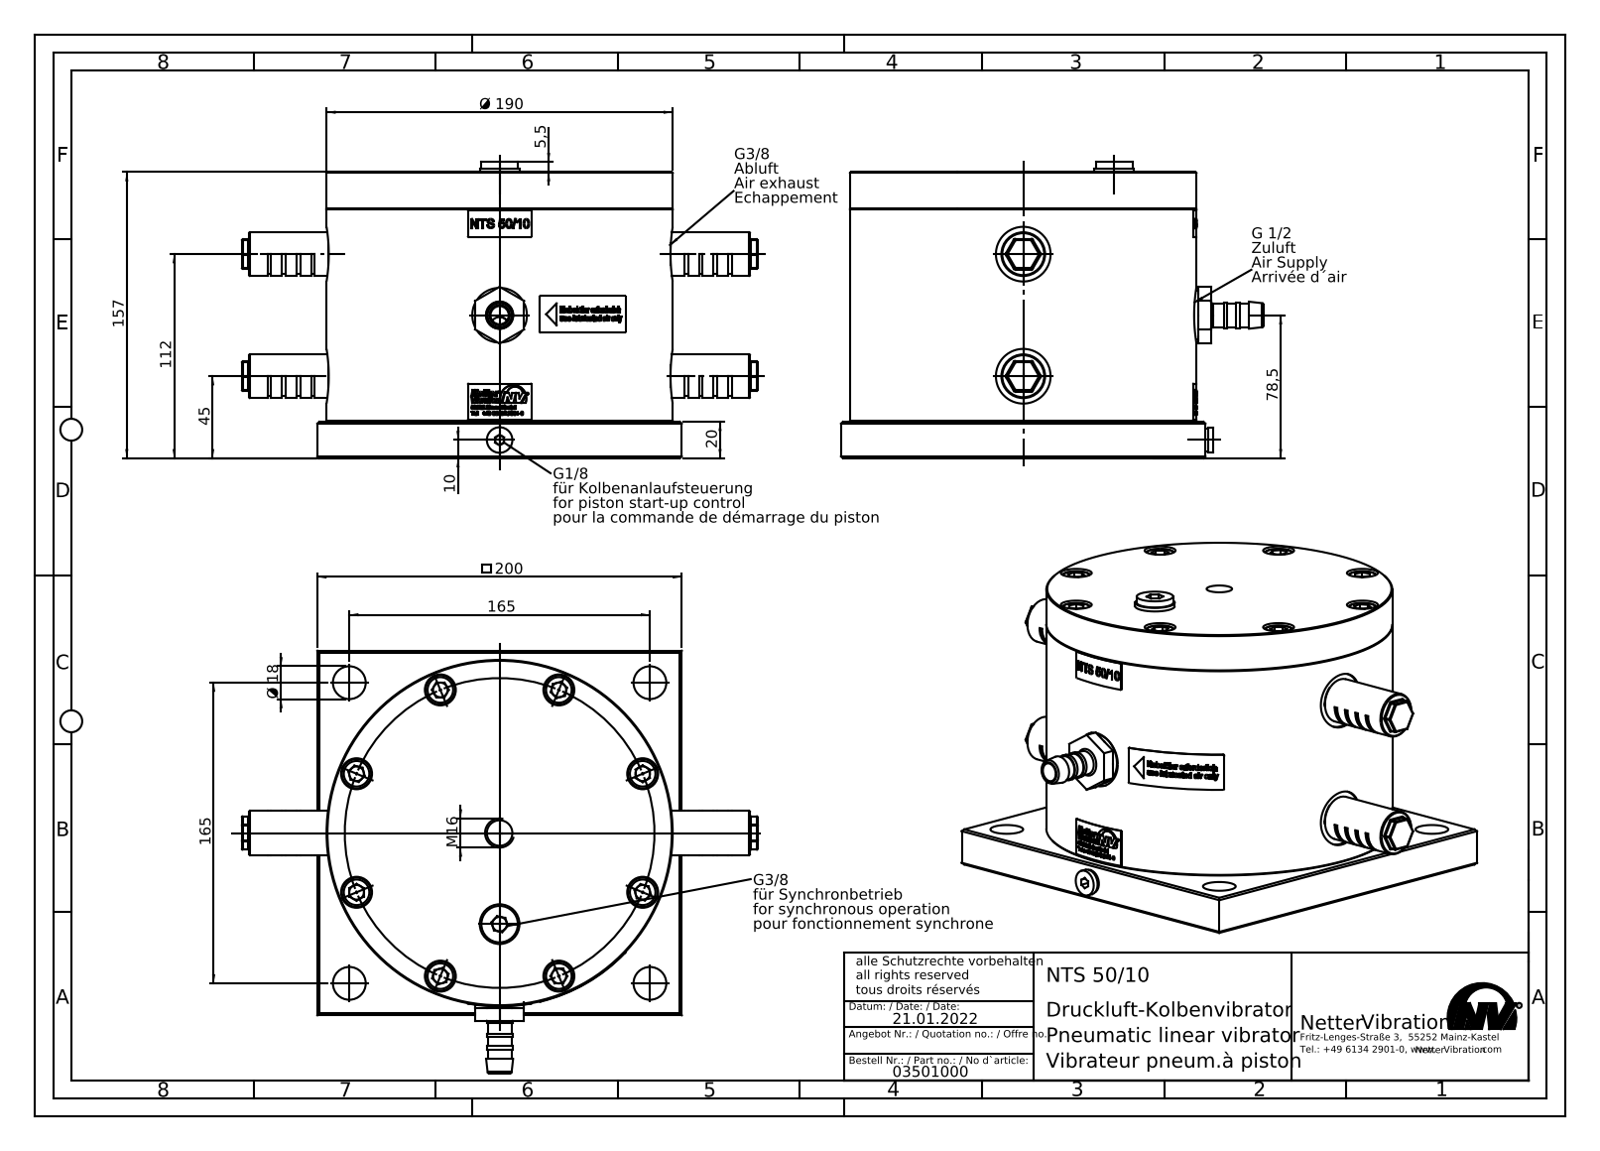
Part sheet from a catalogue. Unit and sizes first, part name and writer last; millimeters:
Units: millimetres
Overall size (bounding box): 283 × 218.5 × 162.5
Round holes (diameter × count): ⌀8.5 ×8, ⌀10.5 ×8, ⌀11 ×8, ⌀17 ×8, ⌀18 ×4, ⌀14.95 ×3, ⌀30 ×3, ⌀6 ×1, ⌀8.57 ×1, ⌀9 ×1, ⌀9.6 ×1, ⌀10 ×1
Round bosses / shafts (diameter × count): ⌀16 ×8, ⌀10 ×8, ⌀24 ×2, ⌀16.66 ×2, ⌀190 ×1, ⌀21.8 ×1, ⌀20.96 ×1, ⌀20 ×1
Partial cylindrical surfaces — rounded edges, fillets, slot ends (radius × count): R0.5 ×72, R11 ×2, R95.2 ×1
Main face-to-face distances: 117, 20, 137, 19, 1, 156, 136, 157, 200, 11
Hole centre spacings: 50.13, 85, 115.1, 120.21, 157.06, 168.61, 197.9, 65.05
Volume: 4 732 000 mm³ · Surface area: 390 551 mm²
Bodies: 31 solids, 1345 faces (437 planar, 542 cylindrical, 366 other)
Part name (STEP PRODUCT): NTS 50-10 Kolbenvibrator #03501000
STEP written by: SolidWorks 2015 (AUTOMOTIVE_DESIGN)
